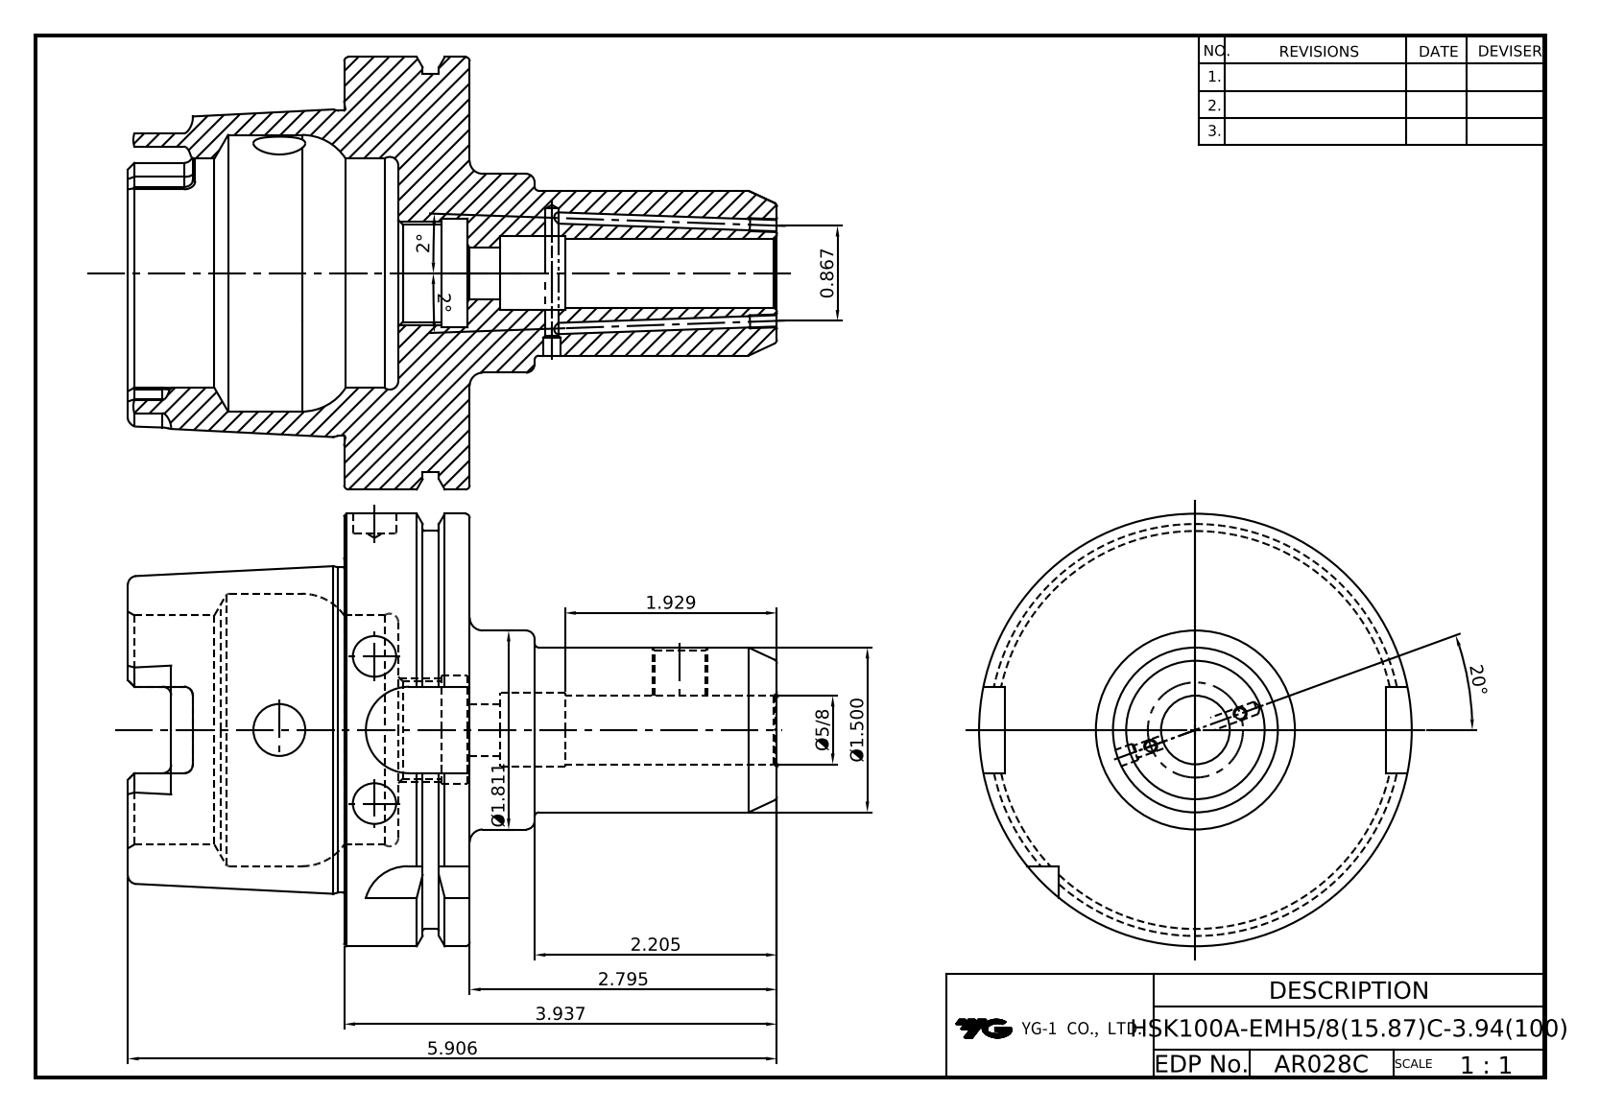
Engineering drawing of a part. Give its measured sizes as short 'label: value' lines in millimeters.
name: LO-HSK100A-EMH15.875C-100
written by: Autodesk Inventor 2022 (AUTOMOTIVE_DESIGN)
unit: mm
bodies: 1 solid, 139 faces (43 planar, 43 cylindrical, 53 other)
size: 150 × 100 × 100
volume: 325 719 mm³; area: 62 491 mm²
holes: 3× ⌀10, 2× ⌀2.46, 2× ⌀12, 1× ⌀3, 1× ⌀4, 1× ⌀11.33, 1× ⌀15.88, 1× ⌀17.07, 1× ⌀22.38, 1× ⌀25, 1× ⌀53, 1× ⌀63
bosses: 1× ⌀100, 1× ⌀92, 1× ⌀75.41, 1× ⌀46, 1× ⌀38.1
rounds: 6× R2, 4× R4.88, 4× R10
face distances: 29, 12.5, 16.5, 79, 62.5, 50, 88, 28.5, 71, 78.5
hole spacings: 41, 70.6
